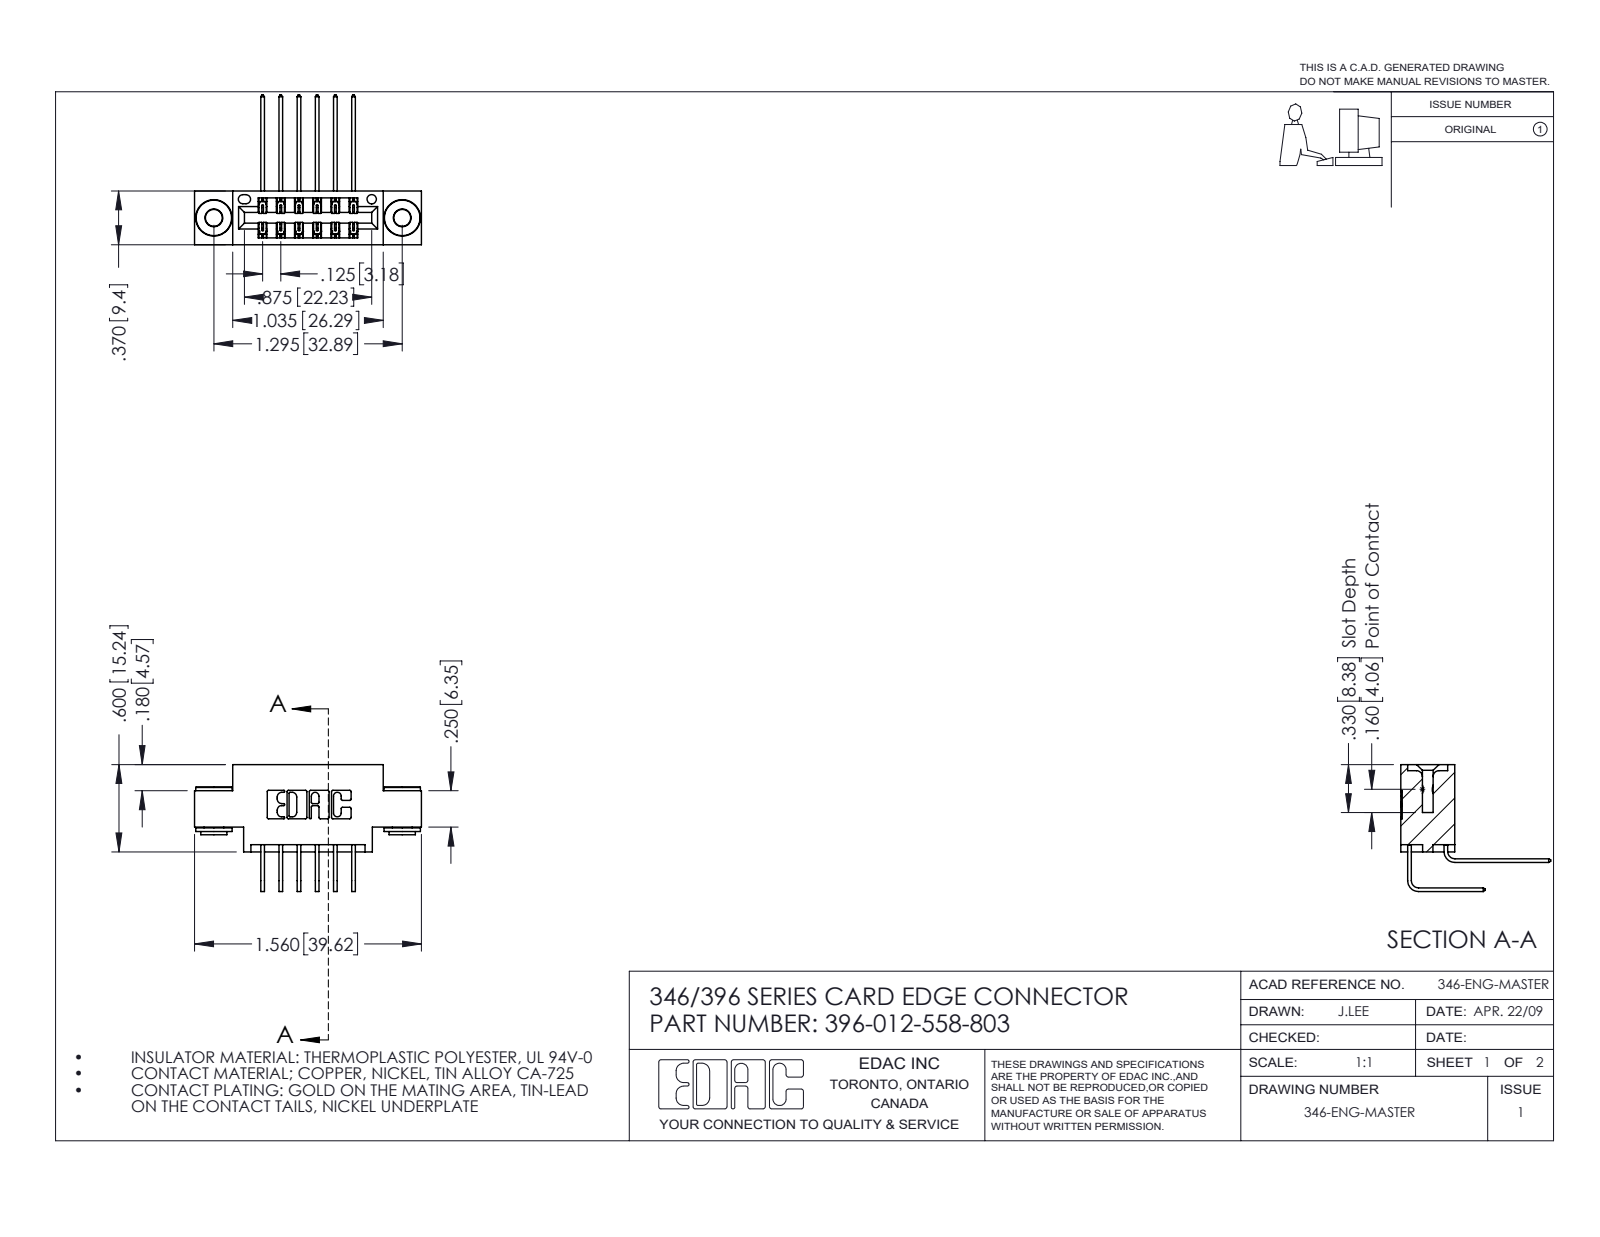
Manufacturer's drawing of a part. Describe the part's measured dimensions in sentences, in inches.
The part is named "345-292-001_558 Tail - 2; 345-250-002_345-250-002-102; 346 Part_0.170 Offset - 0.156 Dia-TH; 345-292-001_558 559 Tail - 1 (+1 more)". Its 3-D file was written by "SolidWorks 2016 (CONFIG_CONTROL_DESIGN)". It is 15 solids with 812 faces: 534 planar, 270 cylindrical and 8 other. Overall it measures 1.56 by 1.03 by 0.873 inches. Its volume is 0.215 cubic inches and its surface area 7.744 square inches. Round holes: 2 of diameter 0.116, 2 of diameter 0.156, 1 of diameter 0.064. Round bosses or shafts: 2 of diameter 0.25, 2 of diameter 0.18, 2 of diameter 0.136. Partial cylindrical surfaces (rounded edges, fillets, slot ends): 22 of radius 0.01, 18 of radius 0.006, 6 of radius 0.007, 6 of radius 0.031, 3 of radius 0.026, 2 of radius 0.014, 2 of radius 0.022, 2 of radius 0.024. The main face-to-face distances are 0.25, 0.37, 0.048, 0.322, 0.025, 0.072, 0.298, 0.275, 0.148, 0.222. The hole center spacings are 0.246, 1.092, 1.295.
